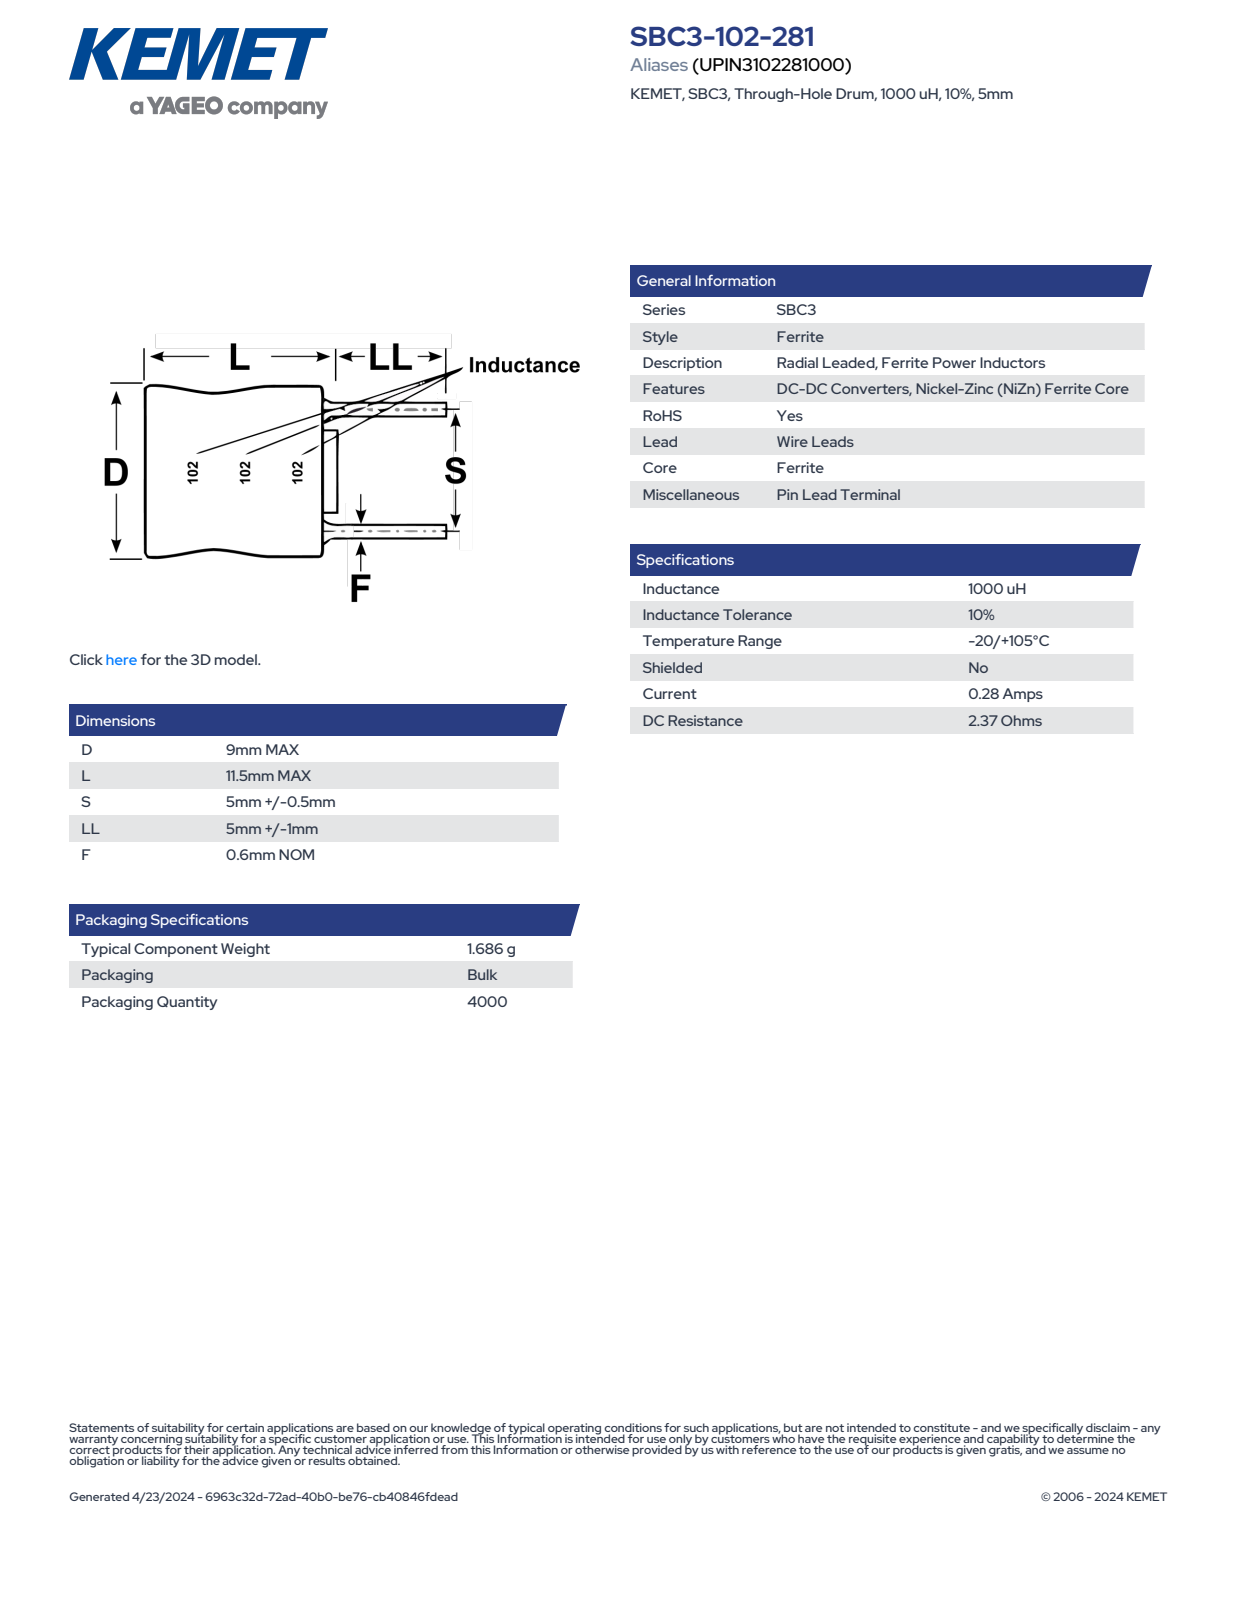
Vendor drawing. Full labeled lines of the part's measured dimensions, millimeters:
Part name (STEP PRODUCT): IL_SBCP_D9L11.5S5LL6F0.6
STEP written by: SolidWorks 2014 (AUTOMOTIVE_DESIGN)
Units: millimetres
Bodies: 4 solids, 84 faces (66 planar, 10 cylindrical, 8 other)
Overall size (bounding box): 17.5 × 9 × 9
Volume: 639 mm³ · Surface area: 459 mm²
Round bosses / shafts (diameter × count): ⌀0.6 ×2, ⌀9 ×1, ⌀8.19 ×1
Main face-to-face distances: 11.16, 11.17, 0.34, 11.5, 11.51, 6, 6.34, 17.5, 17.51, 3.34
